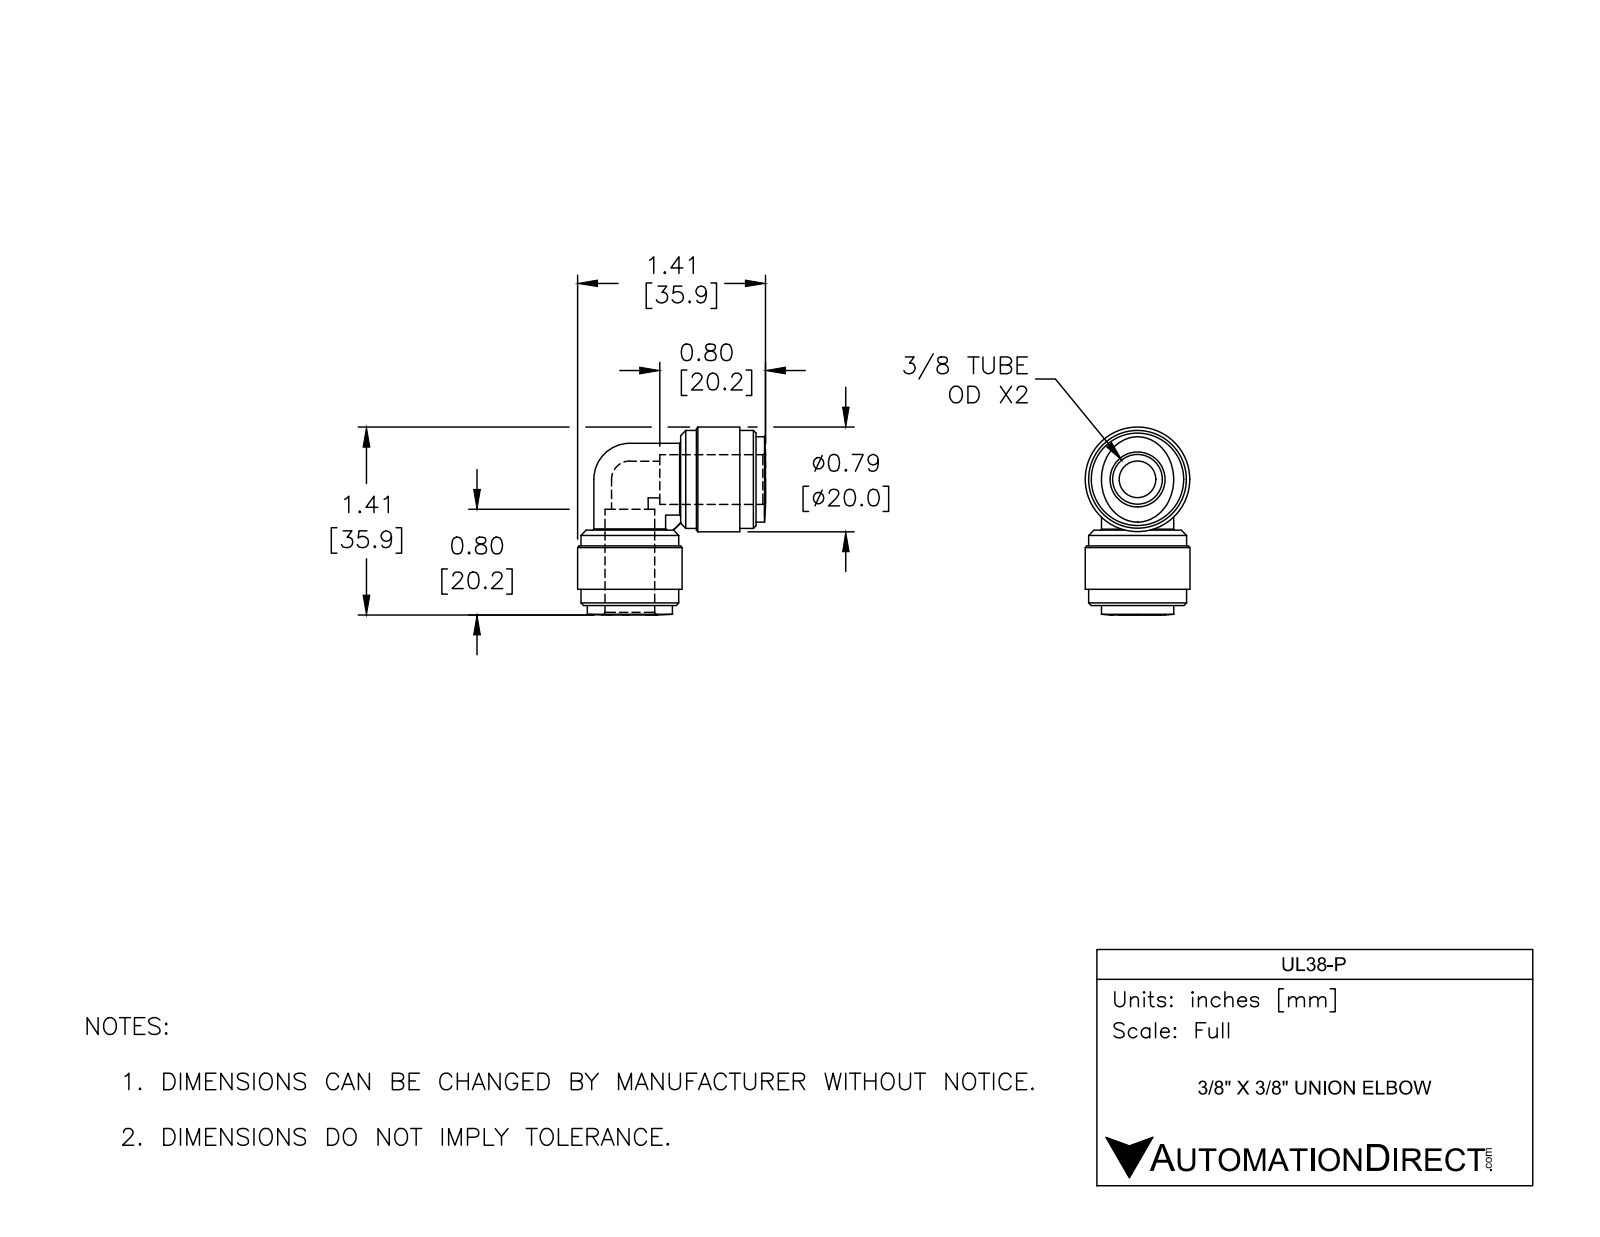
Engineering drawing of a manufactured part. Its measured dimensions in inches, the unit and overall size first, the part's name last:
Units: inches
Overall size (bounding box): 1.413 × 1.413 × 0.787
Round holes (diameter × count): ⌀0.276 ×2, ⌀0.374 ×2
Round bosses / shafts (diameter × count): ⌀0.787 ×2, ⌀0.736 ×2, ⌀0.543 ×2
Main face-to-face distances: 0.567, 0.445, 0.122, 0.157, 0.602, 0.724, 0.276, 0.118, 0.327, 0.449
Volume: 0.527 in³ · Surface area: 7.587 in²
Bodies: 1 solid, 69 faces (12 planar, 24 cylindrical, 33 other)
Part name (STEP PRODUCT): UL38-P
STEP written by: SolidWorks 2017 (AUTOMOTIVE_DESIGN)
